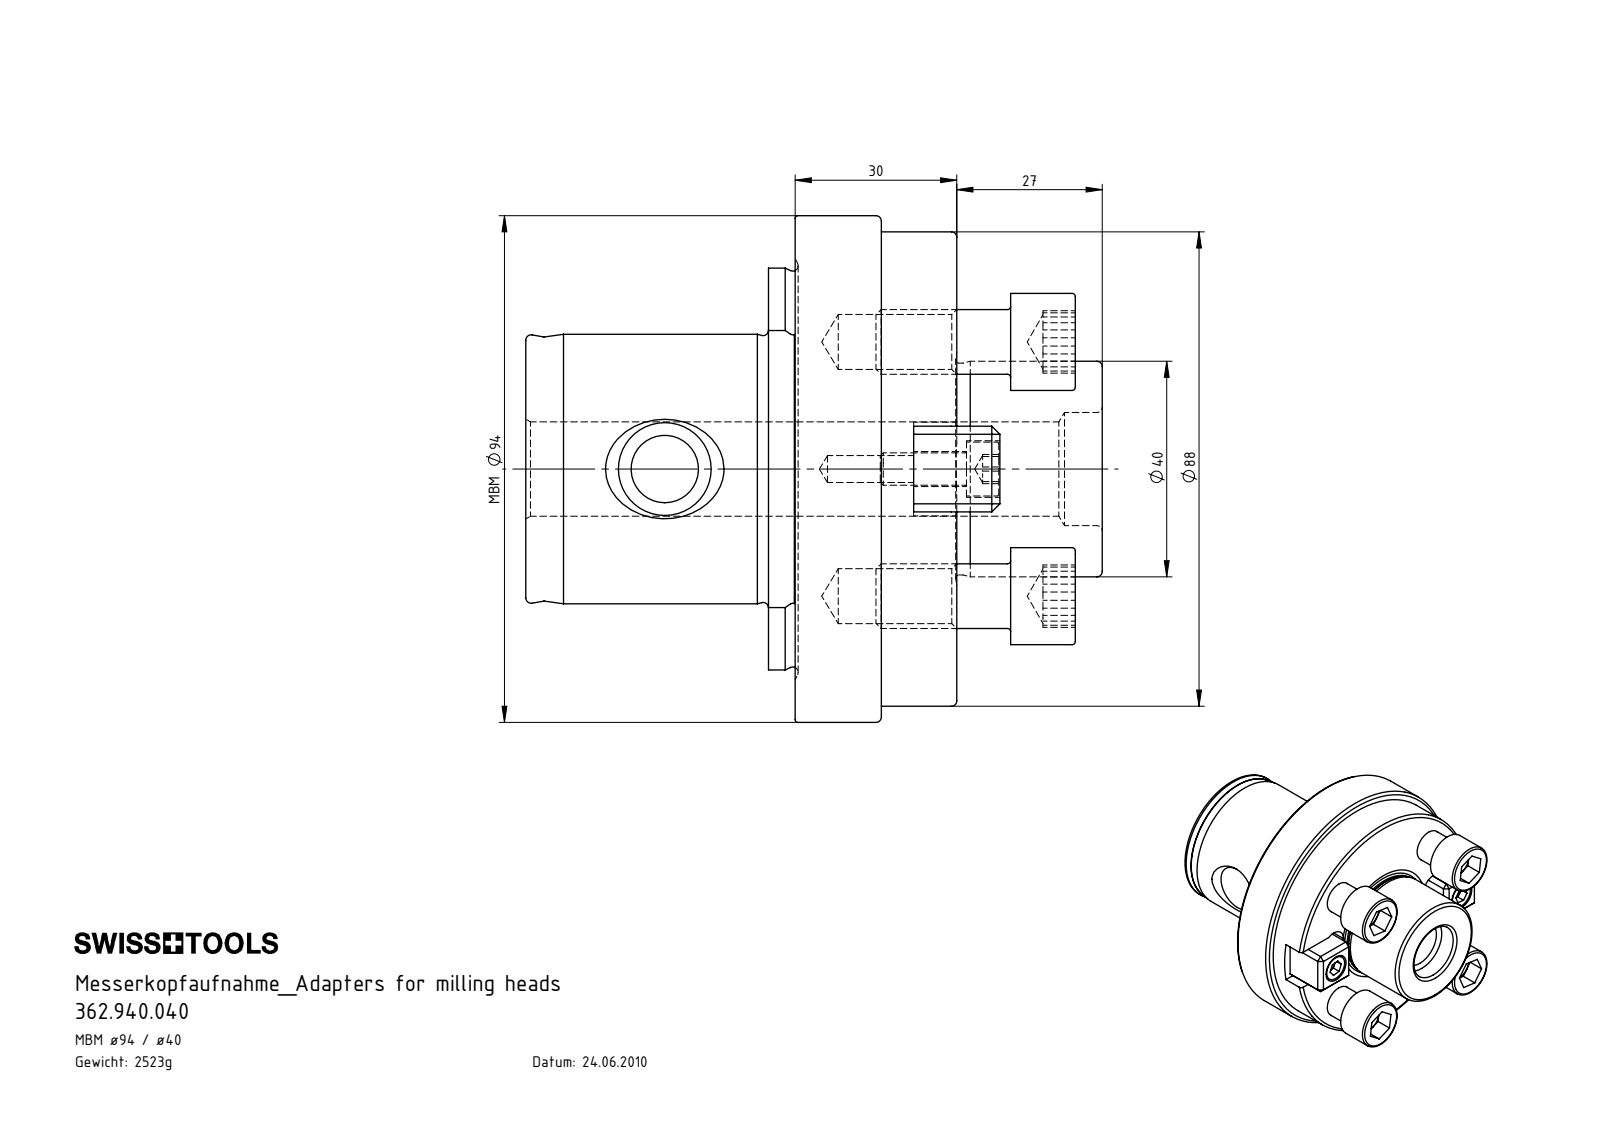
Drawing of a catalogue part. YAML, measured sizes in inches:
part_name: "Ko1-ER1.001.016_A; MB9-D40.002.030_B; ISO 4762 - M6 x 16_PreviewCfg; ISO 4762 - M12 x 25_PreviewCfg (+1 more)"
step_written_by: "SolidWorks 2017 (AUTOMOTIVE_DESIGN)"
units: inches
bodies: {solids: 9, faces: 241, planar: 147, cylindrical: 36, other: 58}
overall_size: [4.213, 3.701, 3.701]
volume: 19.61
surface_area: 89.32
round_holes:
  - {diameter: 0.402, count: 4}
  - {diameter: 0.197, count: 2}
  - {diameter: 0.256, count: 2}
  - {diameter: 0.413, count: 2}
  - {diameter: 0.492, count: 1}
  - {diameter: 0.689, count: 1}
  - {diameter: 0.827, count: 1}
round_bosses_or_shafts:
  - {diameter: 0.709, count: 4}
  - {diameter: 0.472, count: 4}
  - {diameter: 0.394, count: 2}
  - {diameter: 0.236, count: 2}
  - {diameter: 3.701, count: 1}
  - {diameter: 3.465, count: 1}
  - {diameter: 1.969, count: 1}
  - {diameter: 1.575, count: 1}
partial_cylinders:
  - {radius: 0.205, count: 4}
  - {radius: 1.467, count: 1}
face_to_face_distances: [1.181, 0.866, 1.376, 0.195, 1.774, 1.969, 3.15, 0.315, 2.835, 1.061]
hole_center_spacings: [1, 1.313, 1.857, 2.413, 1.299, 2.626, 2.598]
